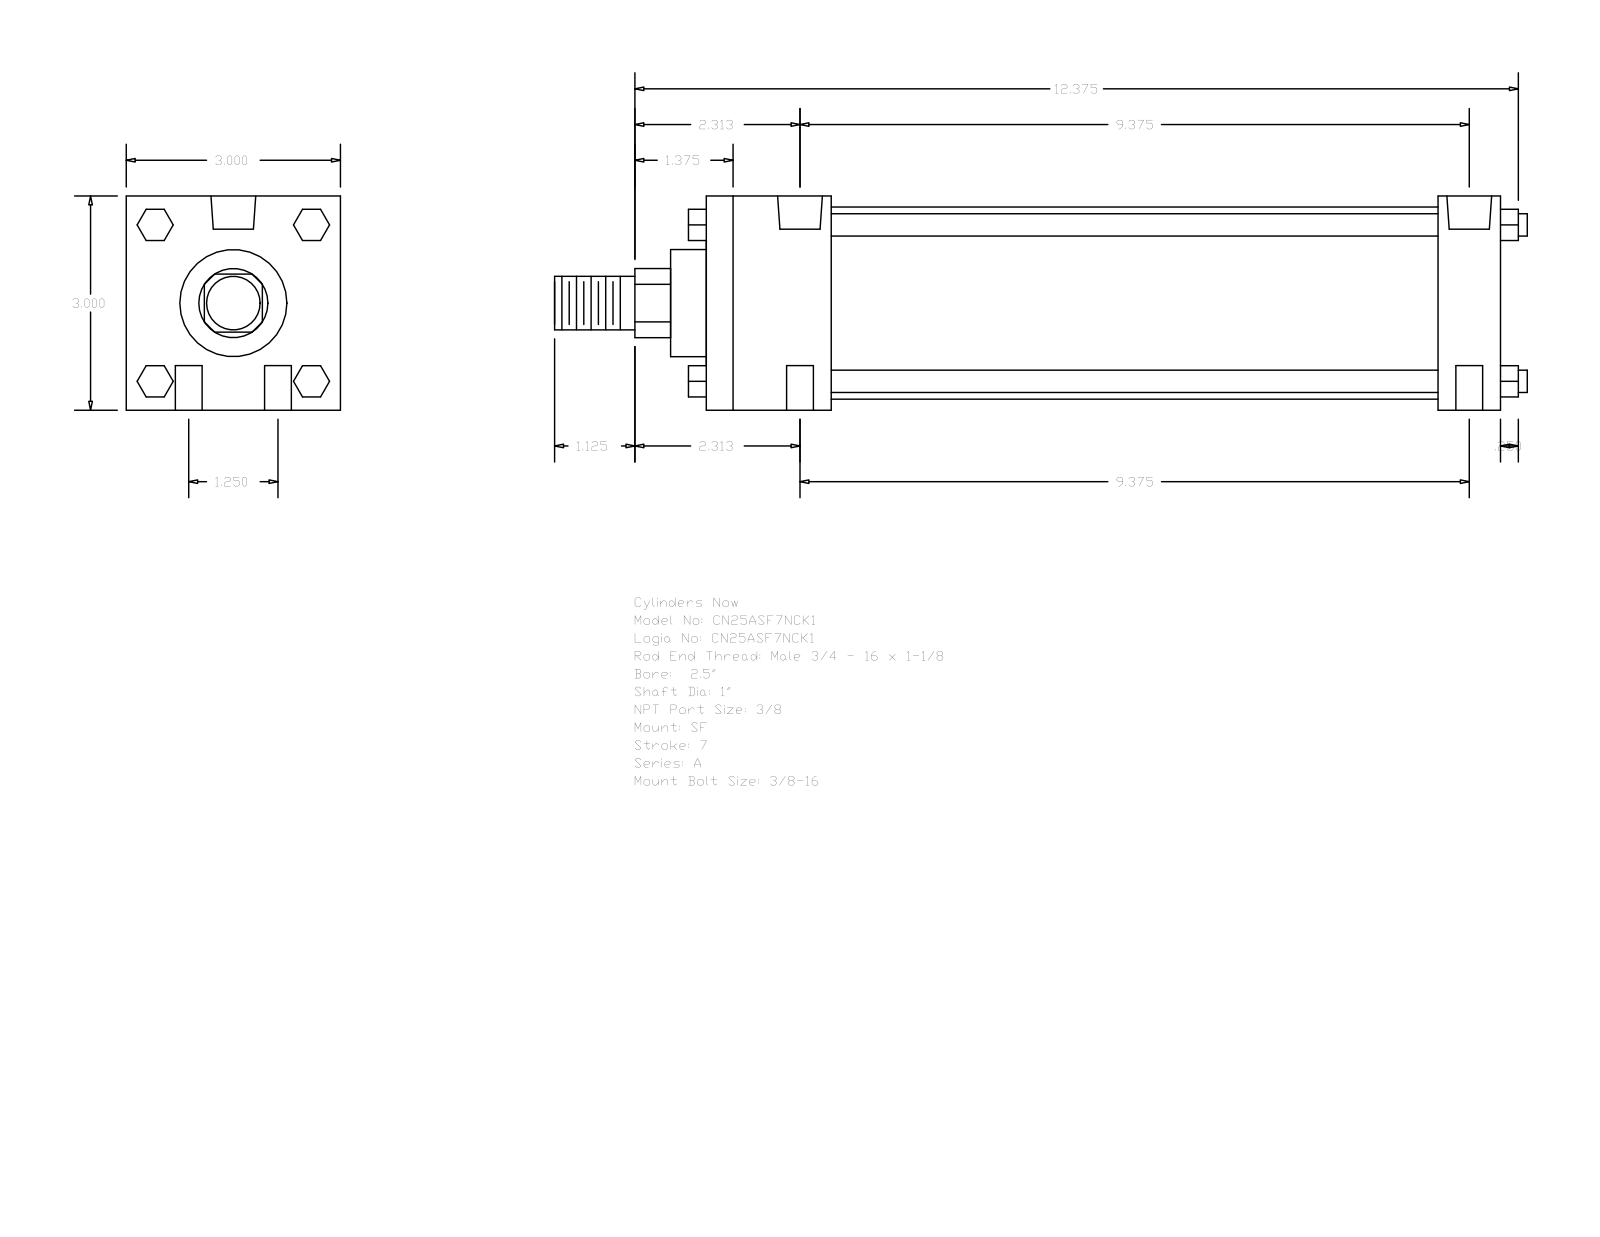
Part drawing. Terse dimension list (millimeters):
name: A_SF__0250_1
written by: GSSL Pune (CONFIG_CONTROL_DESIGN)
unit: mm
bodies: 0 solids, 124 faces (94 planar, 30 cylindrical, 0 other)
size: 346.07 × 76.2 × 76.2
holes: 4× ⌀9.53, 2× ⌀5.56, 2× ⌀15.93
bosses: 4× ⌀7.94, 1× ⌀68.33, 1× ⌀38.1, 1× ⌀25.4, 1× ⌀19.05
rounds: 1× R12.29
face distances: 76.2, 282.58, 260.35, 22.23, 44.45, 215.9, 238.13, 12.7, 11.11, 57.15
hole spacings: 15.88, 238.65, 238.12, 31.76, 240.23, 242.88
